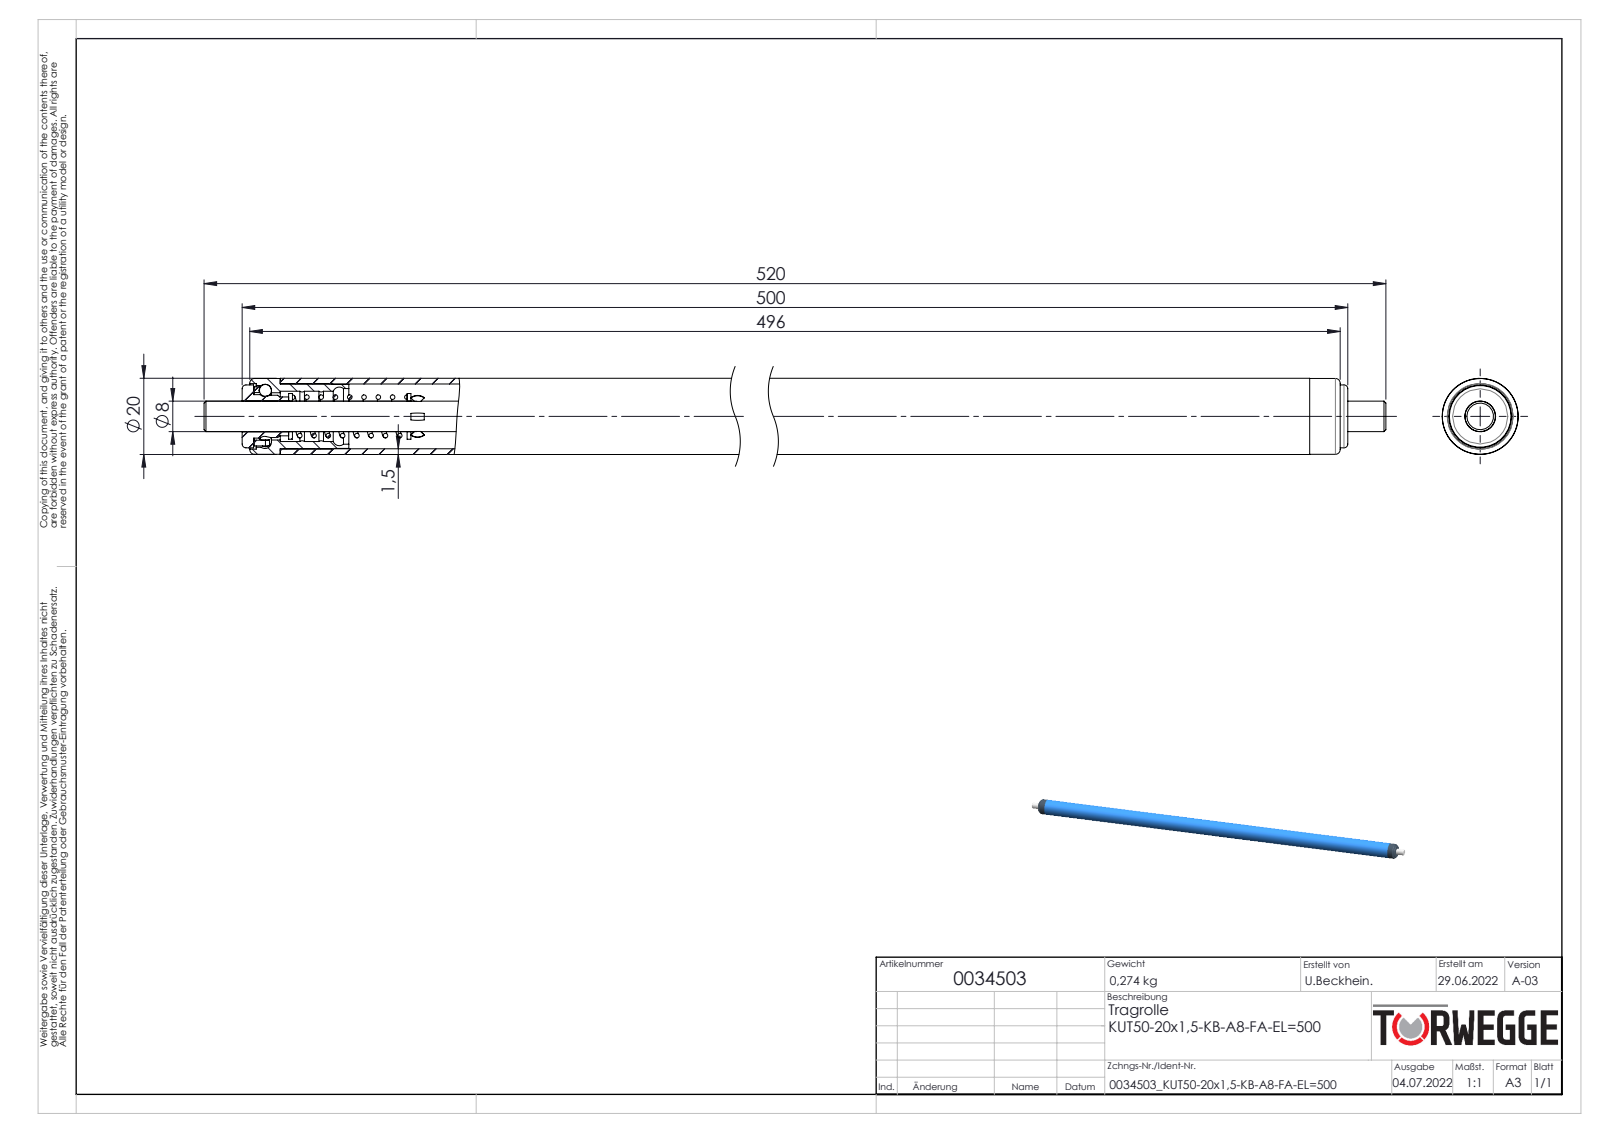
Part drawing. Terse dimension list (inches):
name: 0034503
written by: SolidWorks 2020 (AUTOMOTIVE_DESIGN)
unit: in
bodies: 30 solids, 420 faces (104 planar, 90 cylindrical, 226 other)
size: 20.472 × 0.787 × 0.787
volume: 4.621 in³; area: 124.4 in²
holes: 1× ⌀0.315, 1× ⌀0.319, 1× ⌀0.488, 1× ⌀0.492, 1× ⌀0.52, 1× ⌀0.575, 1× ⌀0.638, 1× ⌀0.669, 1× ⌀0.677
bosses: 1× ⌀0.787, 1× ⌀0.783, 1× ⌀0.673, 1× ⌀0.661, 1× ⌀0.65, 1× ⌀0.61, 1× ⌀0.472, 1× ⌀0.449
face distances: 0.394, 19.291, 0.118, 19.567, 0.276, 19.173, 0.039, 19.685, 0.48, 19.205
